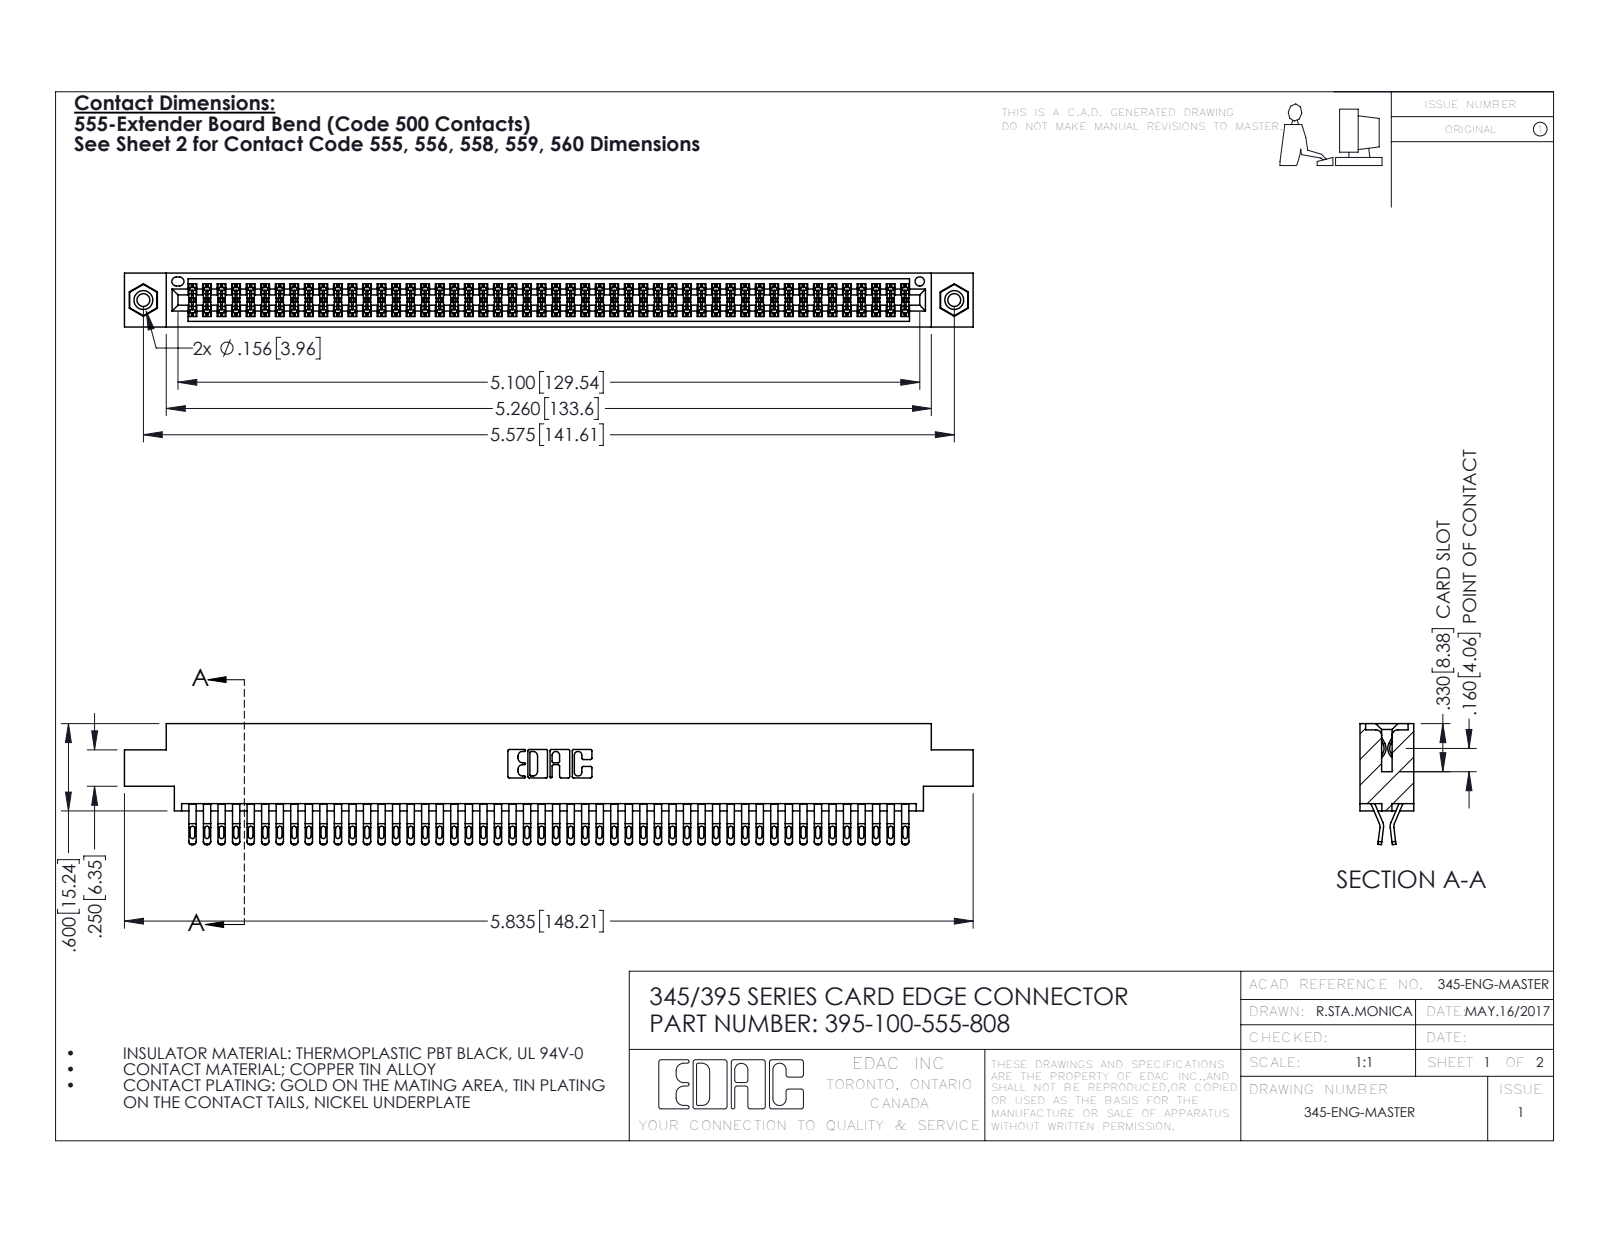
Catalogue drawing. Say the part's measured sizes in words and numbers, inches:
The part is named "345-250-001_345-250-003-102; 395-100-555-808; 345-292-001_555 Tail; 345 Part_0.170 Offset - 0.156 Dia-TI". Its 3-D file was written by "SolidWorks 2016 (CONFIG_CONTROL_DESIGN)". It is 103 solids with 5790 faces: 3216 planar, 2558 cylindrical and 16 other. Overall it measures 5.835 by 0.832 by 0.37 inches. Its volume is 0.893 cubic inches and its surface area 35.59 square inches. Round holes: 2 of diameter 0.089, 2 of diameter 0.125, 2 of diameter 0.156, 1 of diameter 0.064. Round bosses or shafts: 2 of diameter 0.155. Partial cylindrical surfaces (rounded edges, fillets, slot ends): 250 of radius 0.016, 200 of radius 0.02, 150 of radius 0.006, 22 of radius 0.01, 6 of radius 0.007, 6 of radius 0.031, 3 of radius 0.026, 2 of radius 0.01. The main face-to-face distances are 0.072, 0.298, 0.37, 0.025, 0.2, 0.098, 0.272, 0.225, 0.175, 0.149. The hole center spacings are 0.27, 5.339, 5.575.
